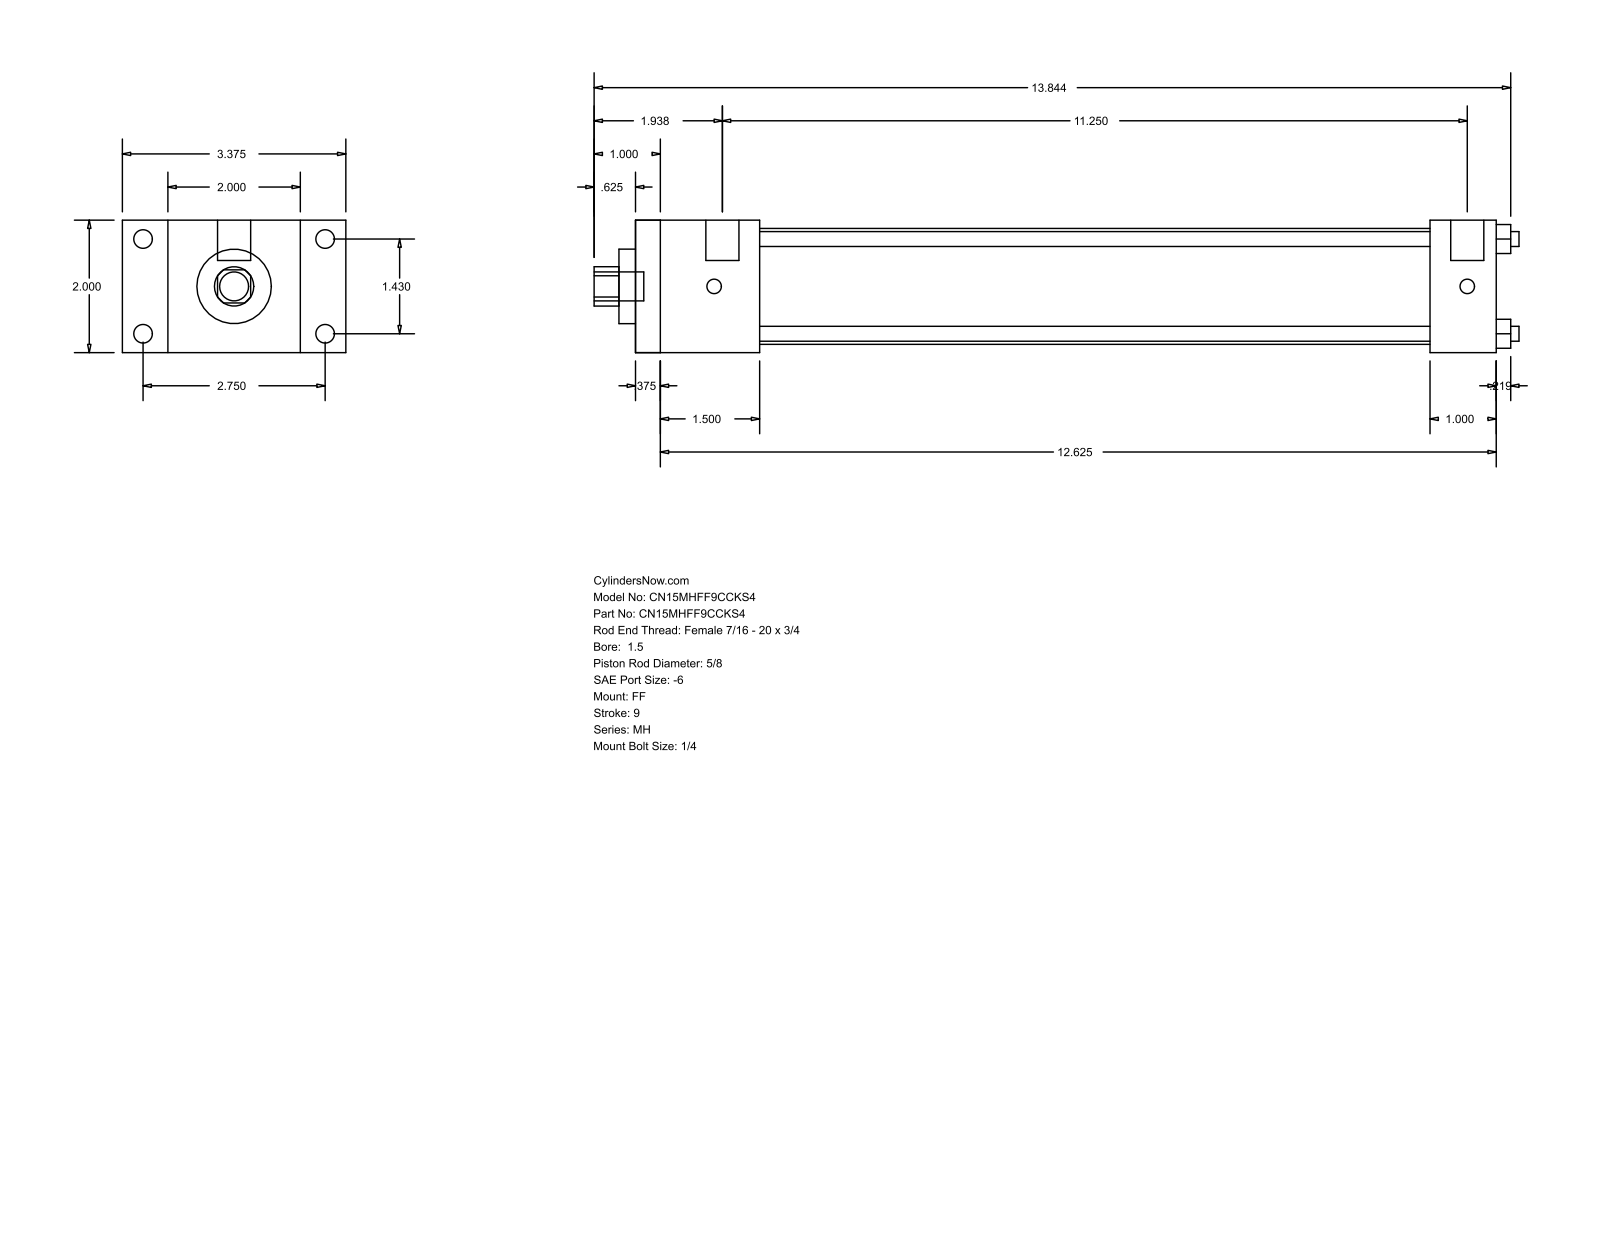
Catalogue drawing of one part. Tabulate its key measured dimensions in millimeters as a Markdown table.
| quantity | value |
| --- | --- |
| part name | MH_FF__0150_0.625 |
| STEP written by | GSSL Pune (CONFIG_CONTROL_DESIGN) |
| units | millimeters |
| bodies | 0 solids, 92 faces (64 planar, 28 cylindrical, 0 other) |
| overall size | 354.81 × 85.72 × 50.8 |
| round holes (diameter × count) | 5.71 × 4, 15.88 × 1, 28.57 × 1, 44.45 × 1 |
| round bosses / shafts (diameter × count) | 7.14 × 4, 5.56 × 4, 12.7 × 2, 11.11 × 1 |
| partial cylindrical surfaces (radius × count) | 7.54 × 1 |
| main face-to-face distances | 50.8, 330.19, 9.52, 320.67, 17.46, 68.26, 47.62, 38.1, 282.57, 304.8 |
| hole center spacings | 25.68, 36.32, 51.36 |
